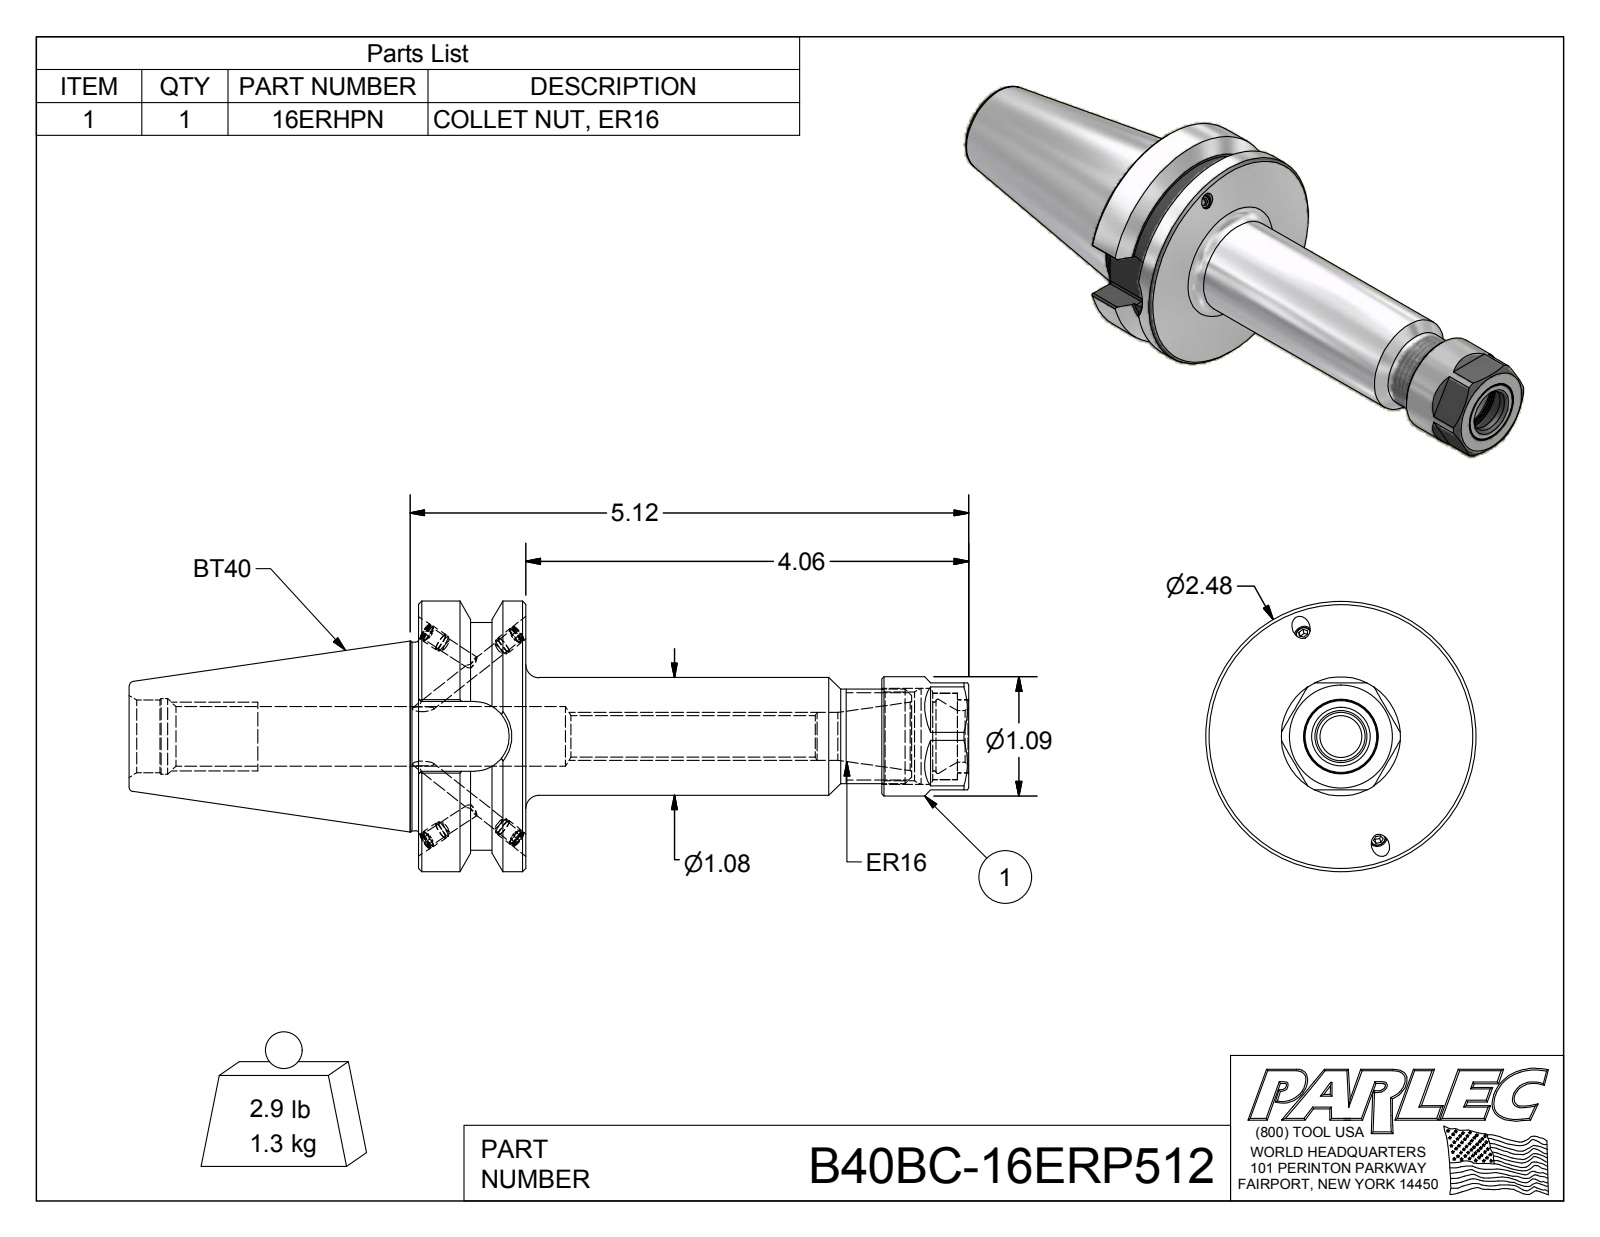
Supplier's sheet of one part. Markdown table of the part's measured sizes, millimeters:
| quantity | value |
| --- | --- |
| part name | B40BC-16ERP512; B40BCB-16ER5-1; 029-965; 16ERHPN |
| STEP written by | Autodesk Inventor 2012 (AUTOMOTIVE_DESIGN) |
| units | millimeters |
| bodies | 7 solids, 194 faces (87 planar, 53 cylindrical, 54 other) |
| overall size | 195.5 × 63 × 63 |
| volume | 165 300 mm³ |
| surface area | 38 770 mm² |
| round holes (diameter × count) | 3.3 × 4, 4.1 × 4, 9.7 × 1, 11.2 × 1, 12 × 1, 13.8 × 1, 16 × 1, 17 × 1, 17.1 × 1, 17.3 × 1, 17.6 × 1, 20.2 × 1 |
| round bosses / shafts (diameter × count) | 4.2 × 4, 4 × 4, 63 × 1, 53 × 1, 43.9 × 1, 27.7 × 1, 27.4 × 1, 22 × 1 |
| partial cylindrical surfaces (radius × count) | 0.5 × 8, 8.1 × 1 |
| main face-to-face distances | 25, 24.9, 45.2, 128.1, 103.1, 4.4, 20.5, 107.8, 82.9, 20.2 |
